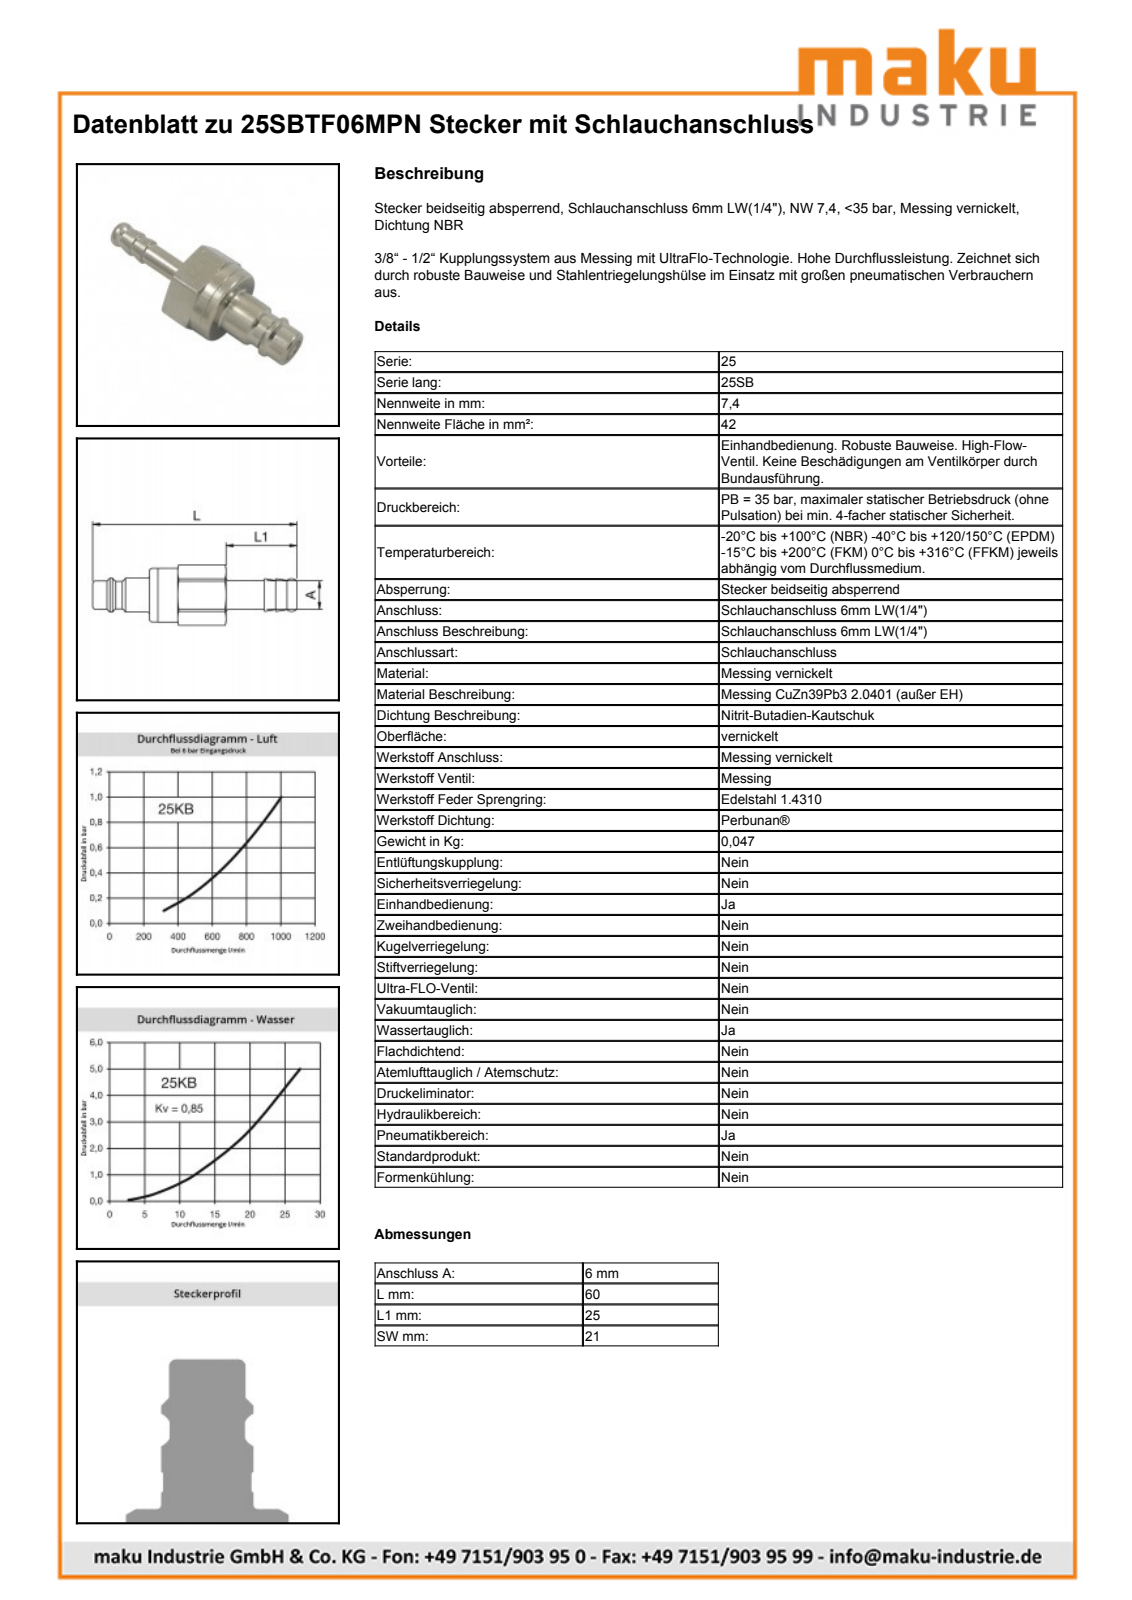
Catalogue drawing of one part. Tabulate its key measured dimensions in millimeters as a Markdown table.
| quantity | value |
| --- | --- |
| part name | D112965 |
| STEP written by | Autodesk Inventor 2013 (AUTOMOTIVE_DESIGN) |
| units | millimeters |
| bodies | 1 solid, 69 faces (20 planar, 20 cylindrical, 29 other) |
| overall size | 72 × 21.32 × 20.11 |
| volume | 10 736 mm³ |
| surface area | 4 248 mm² |
| round holes (diameter × count) | 15.1 × 1, 15.6 × 1 |
| round bosses / shafts (diameter × count) | 19 × 1, 18.95 × 1, 18.75 × 1, 14.75 × 1, 14.5 × 1, 12 × 1, 9.9 × 1, 9.75 × 1 |
| partial cylindrical surfaces (radius × count) | 10.7 × 1 |
| main face-to-face distances | 19, 18.98, 27, 47, 20, 25, 72, 52, 23, 24 |
